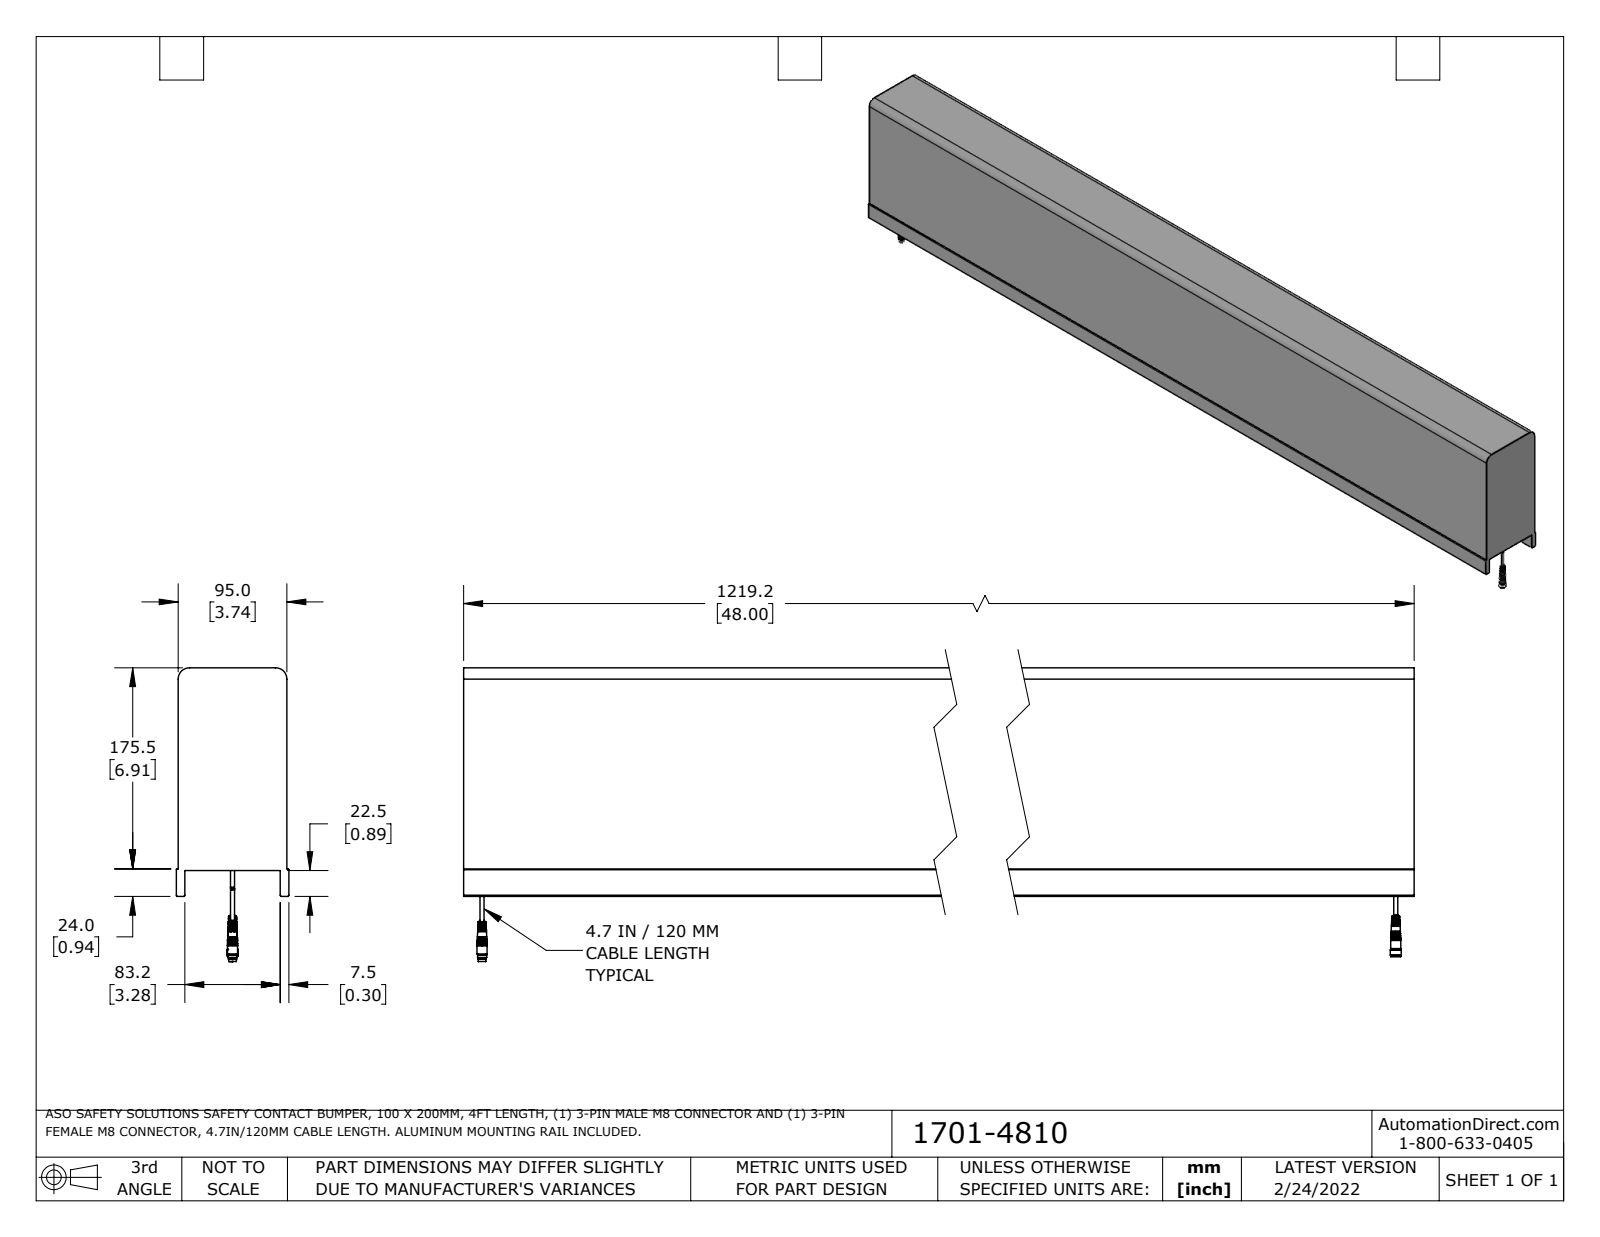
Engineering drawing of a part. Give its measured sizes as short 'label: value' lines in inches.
name: 1701-4810_Default
written by: SolidWorks 2021 (CONFIG_CONTROL_DESIGN)
unit: in
bodies: 24 solids, 447 faces (175 planar, 154 cylindrical, 118 other)
size: 48 × 10.096 × 3.868
volume: 1 273 in³; area: 1 253 in²
holes: 4× ⌀0.047, 3× ⌀0.033, 3× ⌀0.063, 2× ⌀0.134, 1× ⌀0.228, 1× ⌀0.232, 1× ⌀0.272, 1× ⌀0.283
bosses: 8× ⌀0.047, 6× ⌀0.039, 4× ⌀0.02, 2× ⌀0.346, 2× ⌀0.224, 2× ⌀0.138, 1× ⌀0.378, 1× ⌀0.354
rounds: 4× R0.039, 2× R0.03, 2× R0.394
face distances: 3.74, 6.969, 0.064, 3.804, 0.295, 3.572, 0.231, 3.509, 3.868, 3.277
hole spacings: 46.74, 0.028, 0.069, 46.671, 46.713, 46.768, 46.809, 0.041
